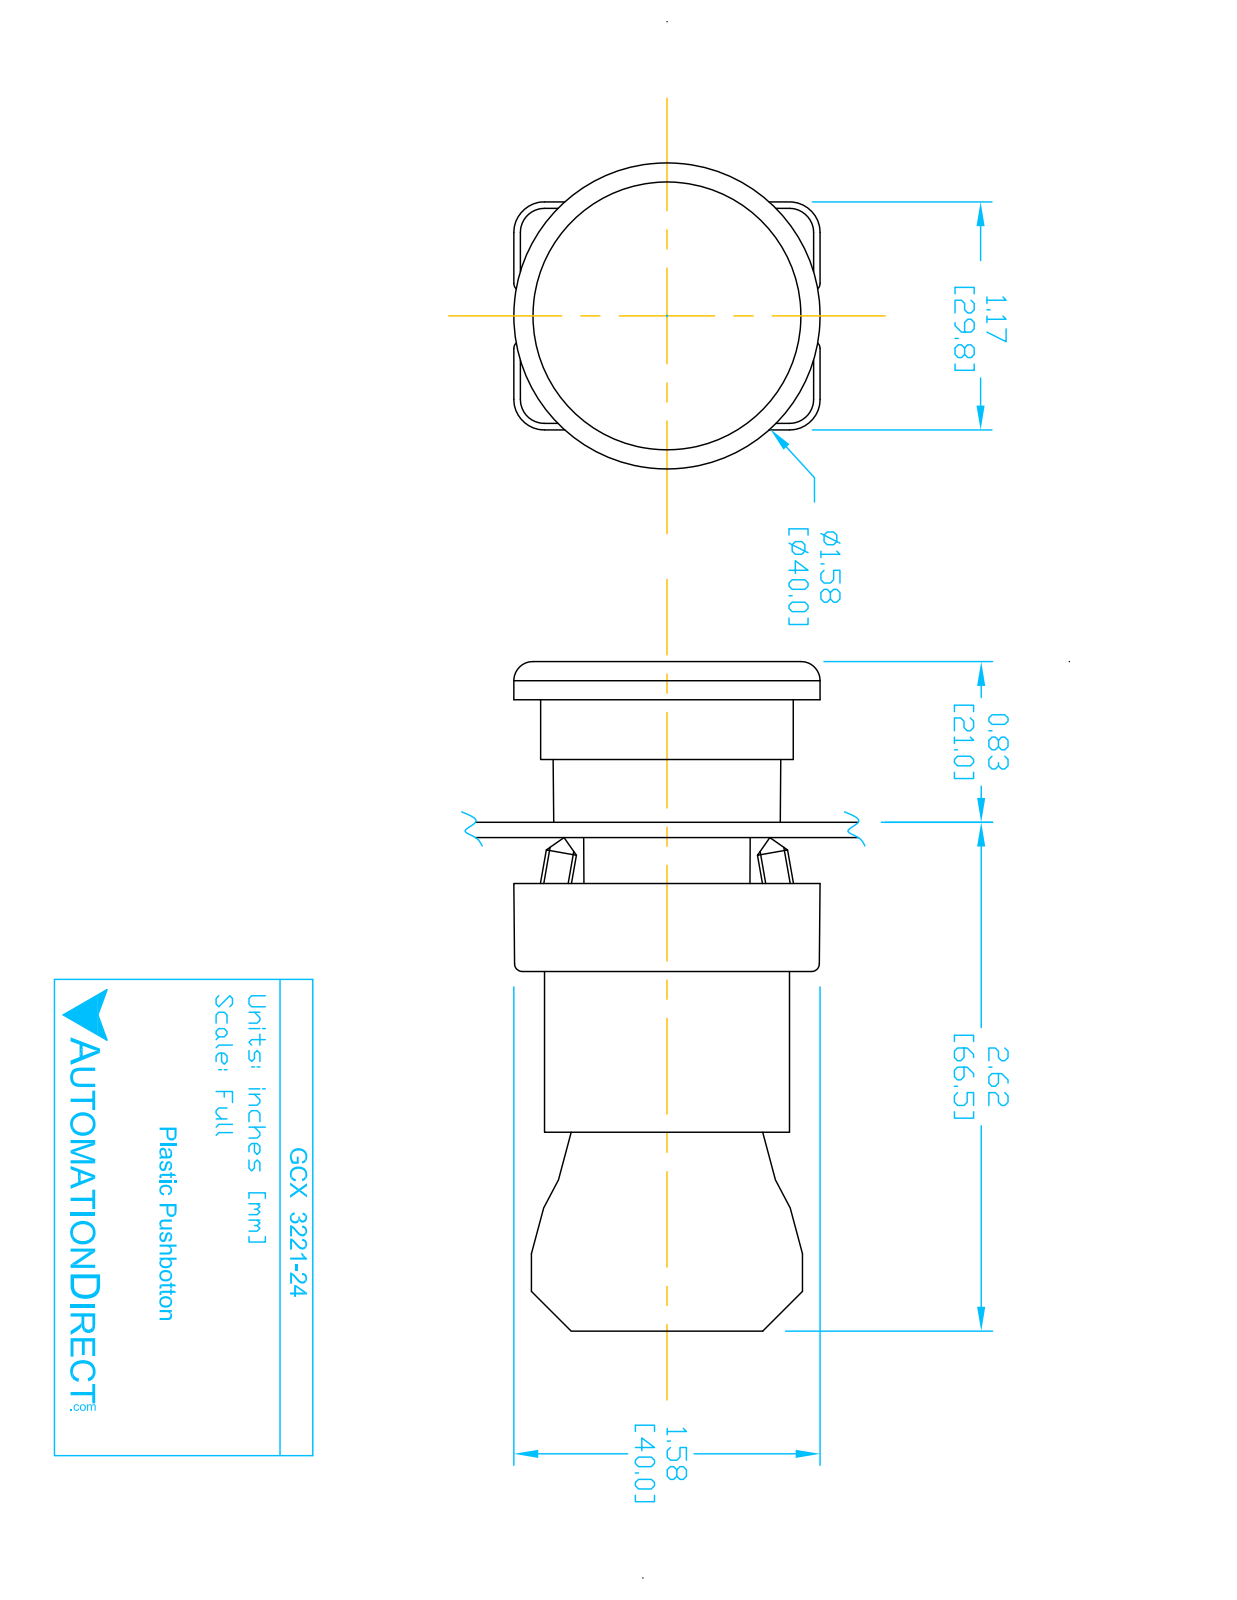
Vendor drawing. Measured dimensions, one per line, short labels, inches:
name: GCX3221-24; GCX322X OPERATOR; ECX1050; ECX3029-2 (+1 more)
written by: SolidWorks 2016 (AUTOMOTIVE_DESIGN)
unit: in
bodies: 7 solids, 431 faces (252 planar, 146 cylindrical, 33 other)
size: 3.469 × 1.581 × 1.575
volume: 2.895 in³; area: 40.89 in²
holes: 2× ⌀0.079, 2× ⌀0.124, 2× ⌀0.13, 1× ⌀0.087, 1× ⌀0.197, 1× ⌀0.469, 1× ⌀0.878, 1× ⌀0.888, 1× ⌀1.024, 1× ⌀1.181
bosses: 4× ⌀0.157, 1× ⌀1.299, 1× ⌀1.175, 1× ⌀0.945, 1× ⌀0.856, 1× ⌀0.78, 1× ⌀0.504
rounds: 24× R0.059, 12× R0.041, 12× R0.124, 12× R0.157, 8× R0.039, 2× R0.128, 1× R0.02, 1× R0.063
face distances: 0.827, 2.445, 1.618, 0.579, 2.287, 1.461, 0.157, 0.587, 0.031, 1.165
hole spacings: 0.236, 0.539, 0.472, 0.484
